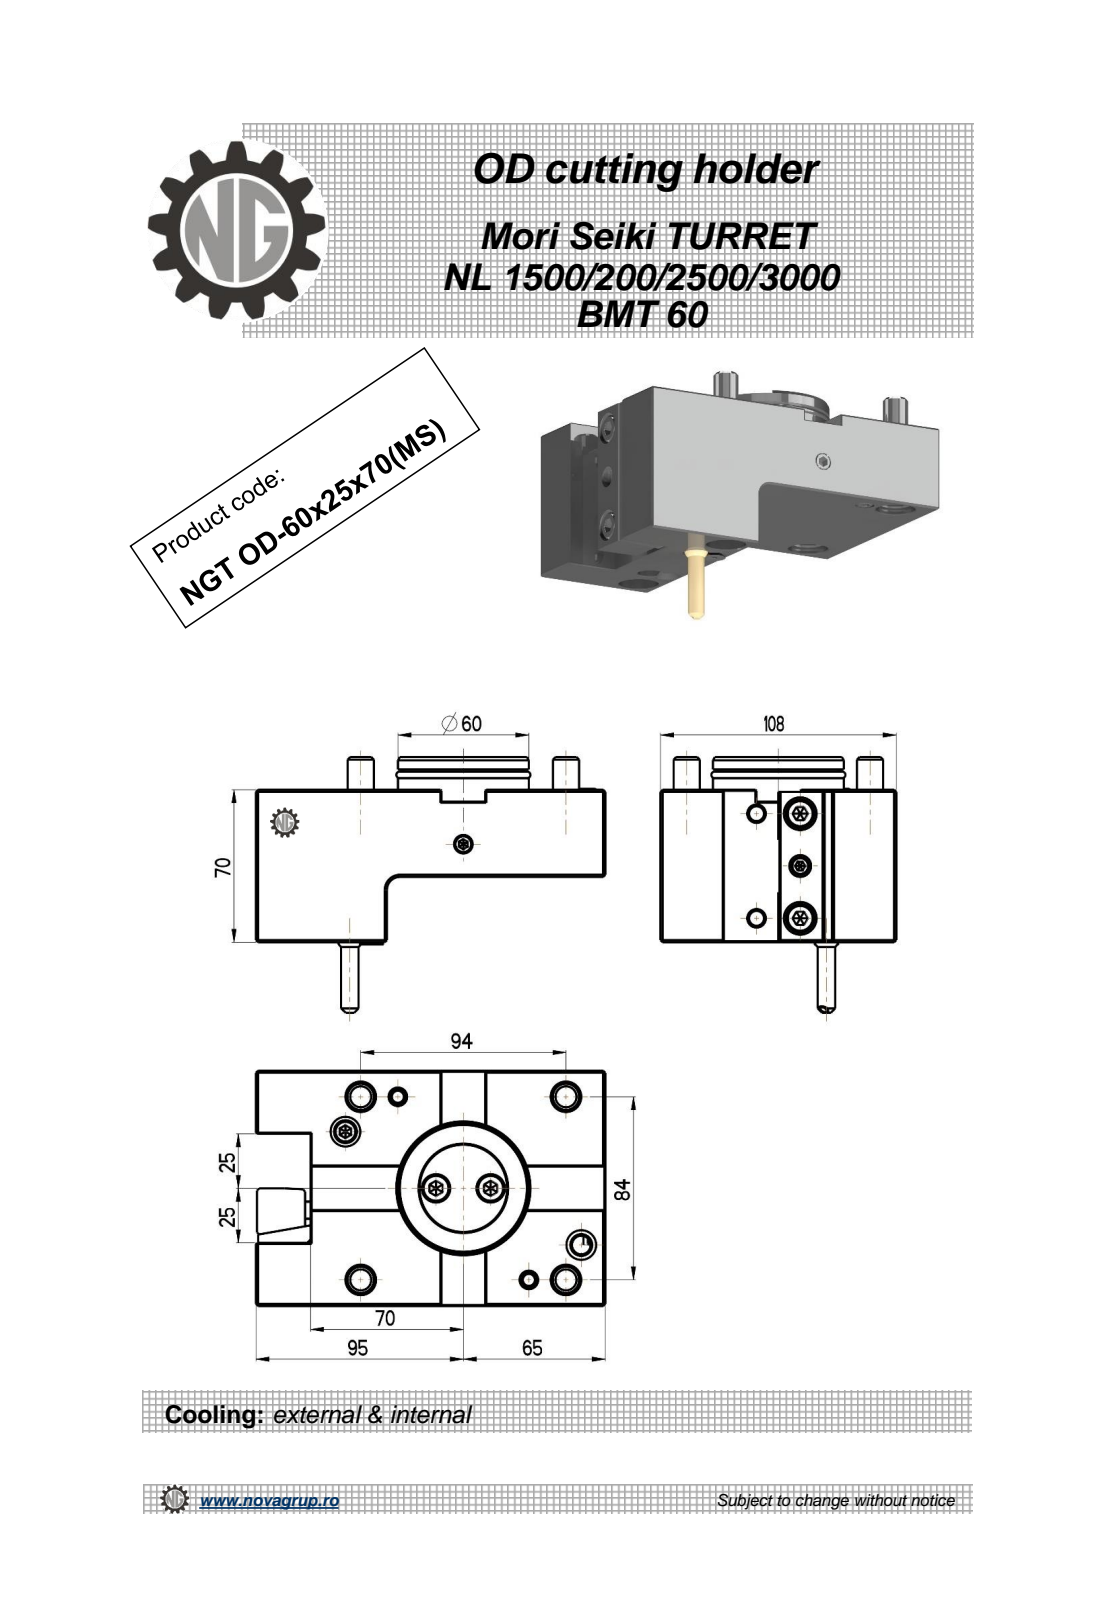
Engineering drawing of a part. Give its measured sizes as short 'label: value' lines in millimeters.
name: NGT_OD_60_25_70_MS
written by: PRO/ENGINEER BY PARAMETRIC TECHNOLOGY CORPORATION, 2010280 (CONFIG_CONTROL_DESIGN)
unit: mm
bodies: 2 solids, 272 faces (155 planar, 65 cylindrical, 52 other)
size: 160 × 117.34 × 108
volume: 860 870 mm³; area: 82 705 mm²
holes: 2× ⌀13.6, 1× ⌀3, 1× ⌀5, 1× ⌀8.5, 1× ⌀40
bosses: 4× ⌀12, 4× ⌀8, 2× ⌀13, 1× ⌀59.9, 1× ⌀55.4, 1× ⌀11.2
rounds: 12× R0.26, 6× R0.22, 6× R0.51, 1× R4, 1× R6
face distances: 40, 108, 70, 30, 160, 25, 35, 135, 60, 5.5
hole spacings: 59.93, 48.04, 56.46, 106.08, 119.87
